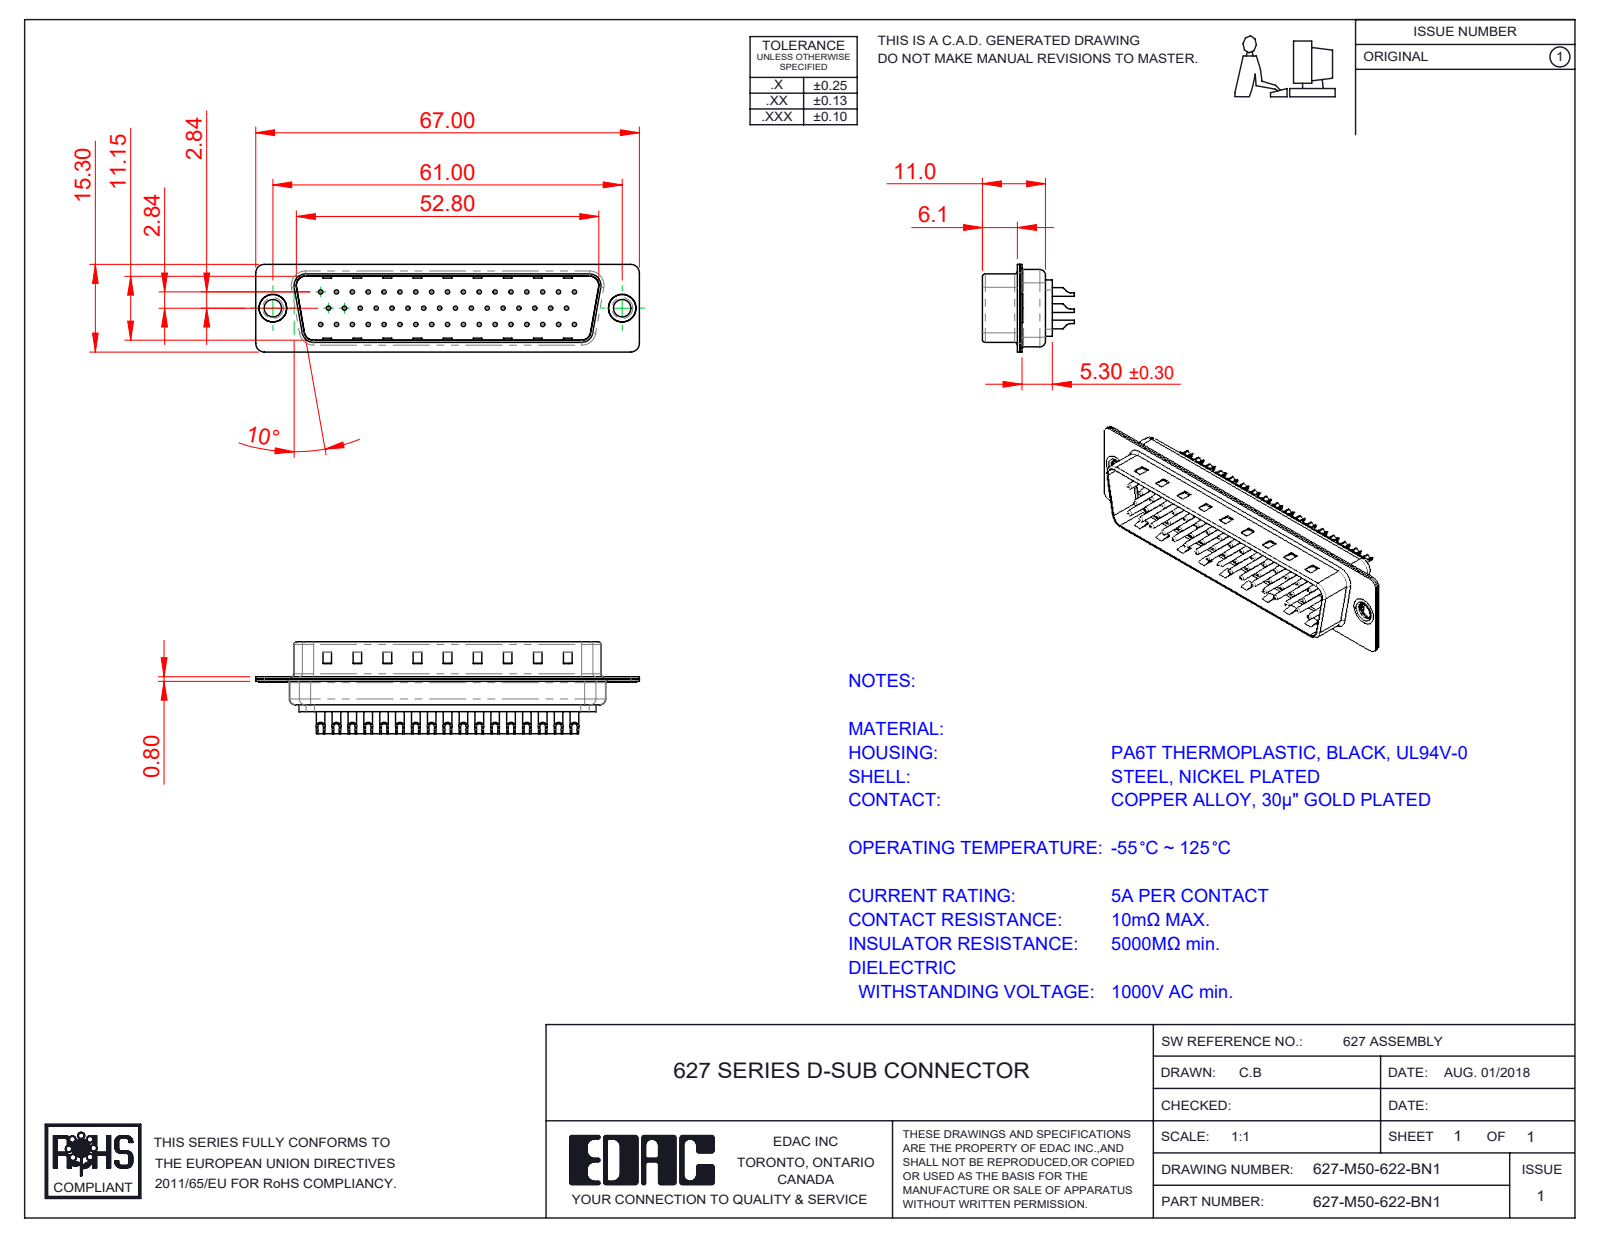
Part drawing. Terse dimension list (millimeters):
name: 627M Shell Front_50 Contacts; 627-M50-622-BN1; 627M Contact Row 1_22; 627M Contact Row 2_22L (+4 more)
written by: SolidWorks 2020 (CONFIG_CONTROL_DESIGN)
unit: mm
bodies: 55 solids, 2236 faces (653 planar, 925 cylindrical, 658 other)
size: 67 × 16.05 × 15.3
volume: 4 561 mm³; area: 11 022 mm²
holes: 50× ⌀0.75, 50× ⌀1, 50× ⌀1.6, 50× ⌀2, 2× ⌀3.05, 2× ⌀4, 2× ⌀4.8
bosses: 50× ⌀1.5, 2× ⌀5, 2× ⌀4.9, 2× ⌀3.55
rounds: 16× R1.5, 12× R2, 8× R0.5, 8× R1.6, 7× R1, 4× R0.25, 4× R0.6, 4× R0.65
face distances: 0.4, 11.55, 5.7, 6.1, 0.78, 0.77, 12.33, 12.32, 13.1, 5.3
hole spacings: 3.16, 2.77, 5.54, 8.31, 11.08, 13.85, 16.62, 5.03
